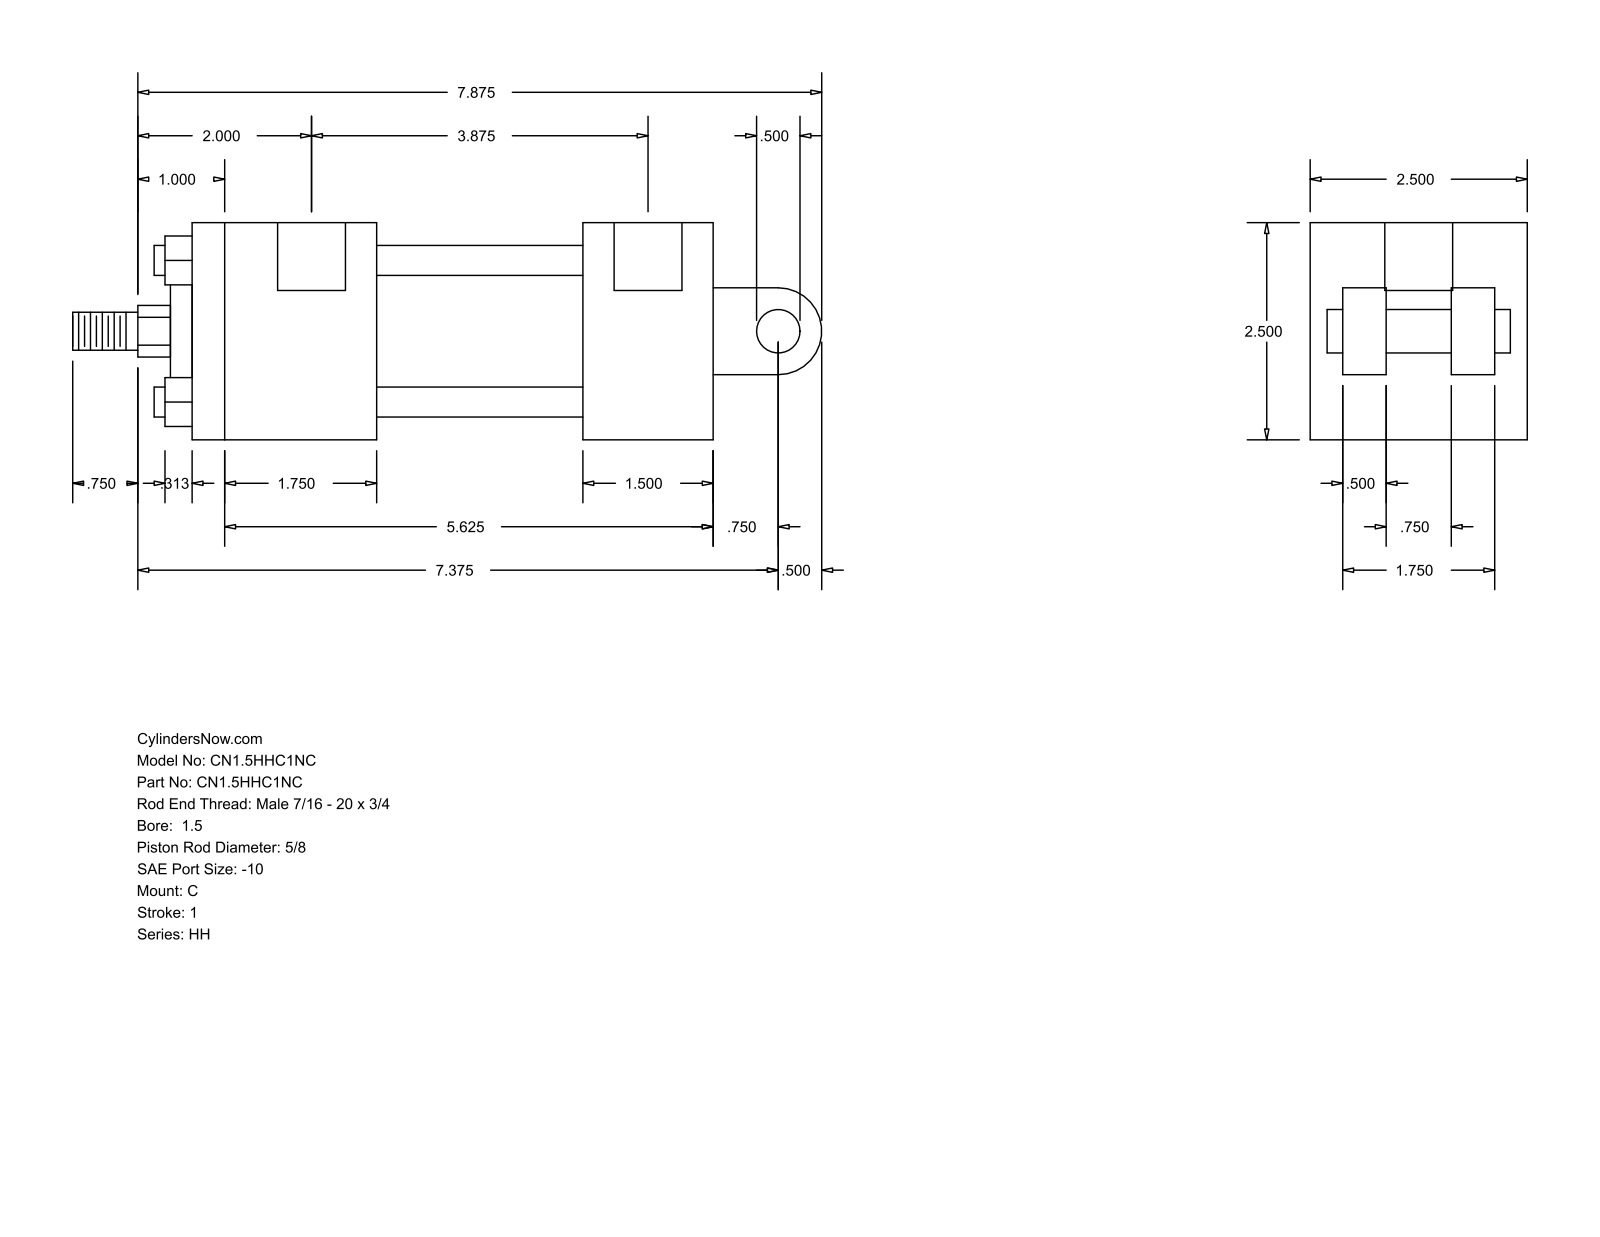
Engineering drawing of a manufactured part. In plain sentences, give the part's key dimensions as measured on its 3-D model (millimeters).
The part is named "HH_C__0150_0.625". Its 3-D file was written by "GSSL Pune (CONFIG_CONTROL_DESIGN)". It is 0 solids with 99 faces: 70 planar, 29 cylindrical and 0 other. Overall it measures 219.07 by 63.5 by 63.5 millimeters. Round holes: 4 of diameter 5.56, 2 of diameter 19.84. Round bosses or shafts: 4 of diameter 8.76, 1 of diameter 44.45, 1 of diameter 28.57, 1 of diameter 15.88, 1 of diameter 12.7, 1 of diameter 11.11. Partial cylindrical surfaces (rounded edges, fillets, slot ends): 1 of radius 7.54, 1 of radius 12.7. The main face-to-face distances are 63.5, 152.4, 38.1, 53.97, 114.3, 60.33, 98.43, 12.7, 19.05, 9.52. The hole center spacings are 1.59, 100.01, 101.6, 98.42.
